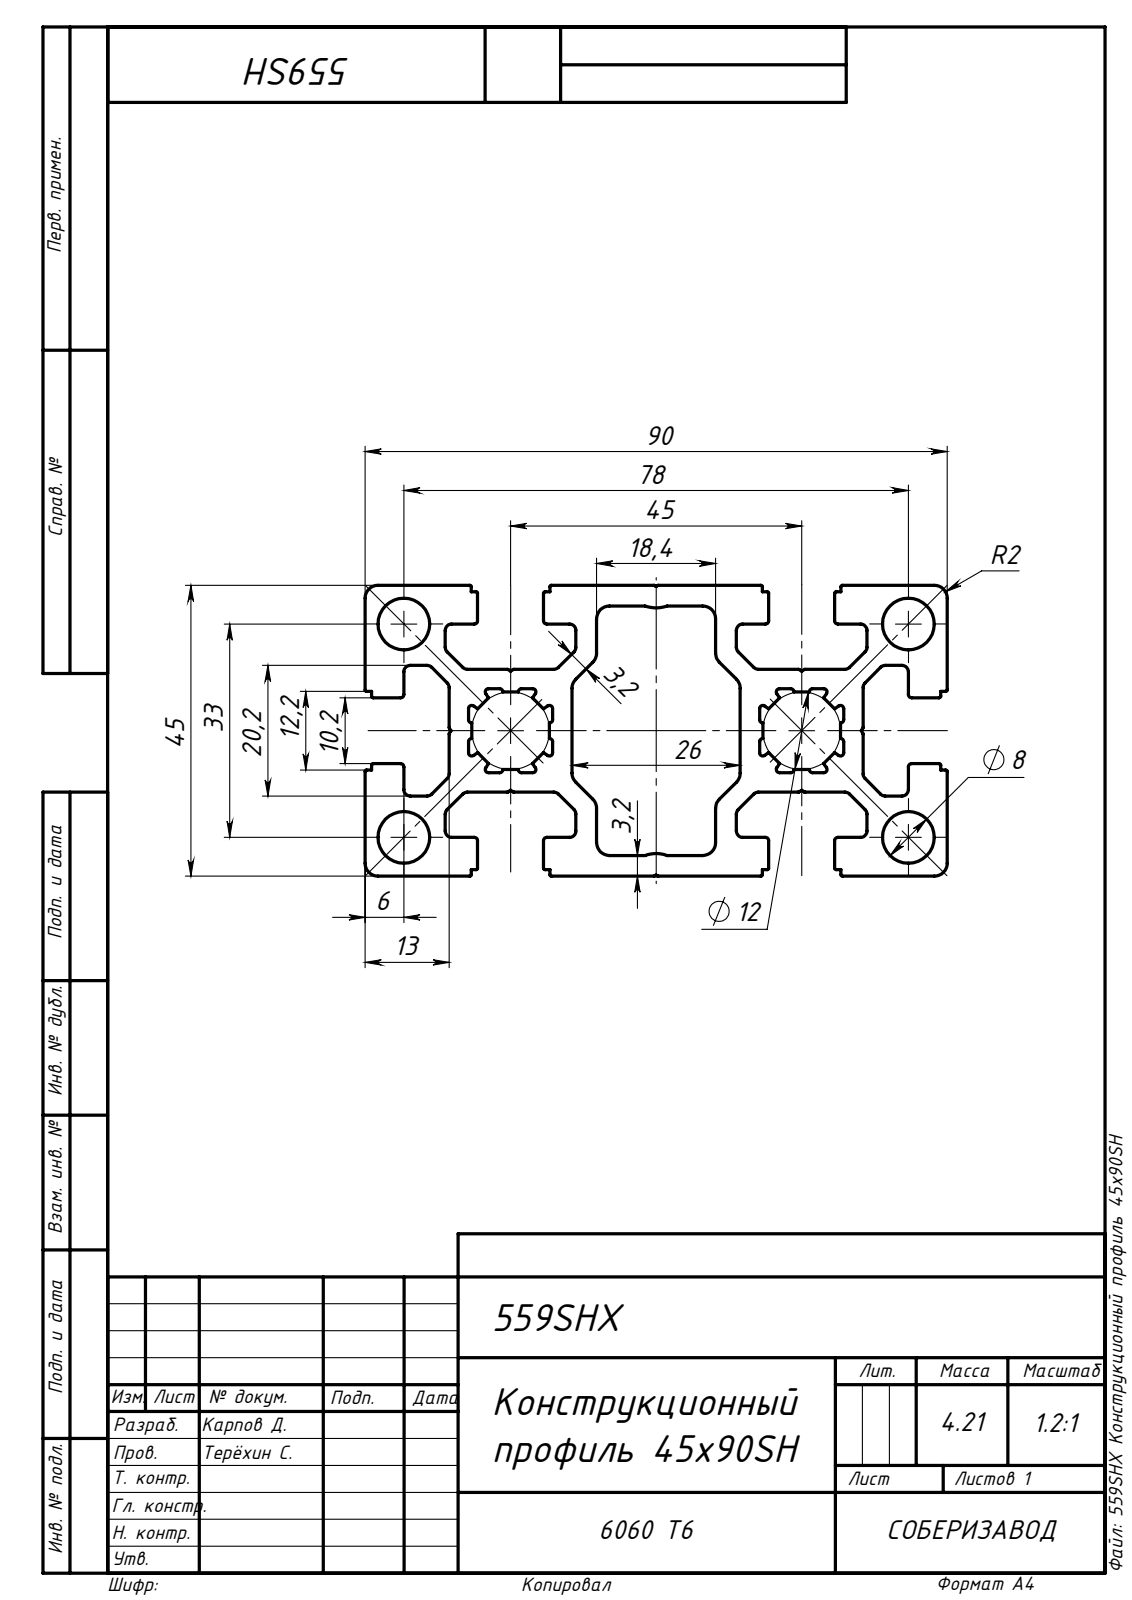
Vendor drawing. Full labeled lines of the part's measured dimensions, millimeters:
STEP written by: SolidWorks 2019 (AUTOMOTIVE_DESIGN)
Units: millimetres
Bodies: 1 solid, 338 faces (176 planar, 162 cylindrical, 0 other)
Overall size (bounding box): 1000 × 90 × 45
Volume: 1 557 000 mm³ · Surface area: 839 436 mm²
Round holes (diameter × count): ⌀8 ×4
Partial cylindrical surfaces — rounded edges, fillets, slot ends (radius × count): R0.5 ×44, R0.25 ×40, R1 ×36, R2 ×16, R5 ×2
Main face-to-face distances: 45, 13, 32, 26, 14.6, 4.4, 19, 26.6, 35.8, 6
Hole centre spacings: 33, 78, 84.69
